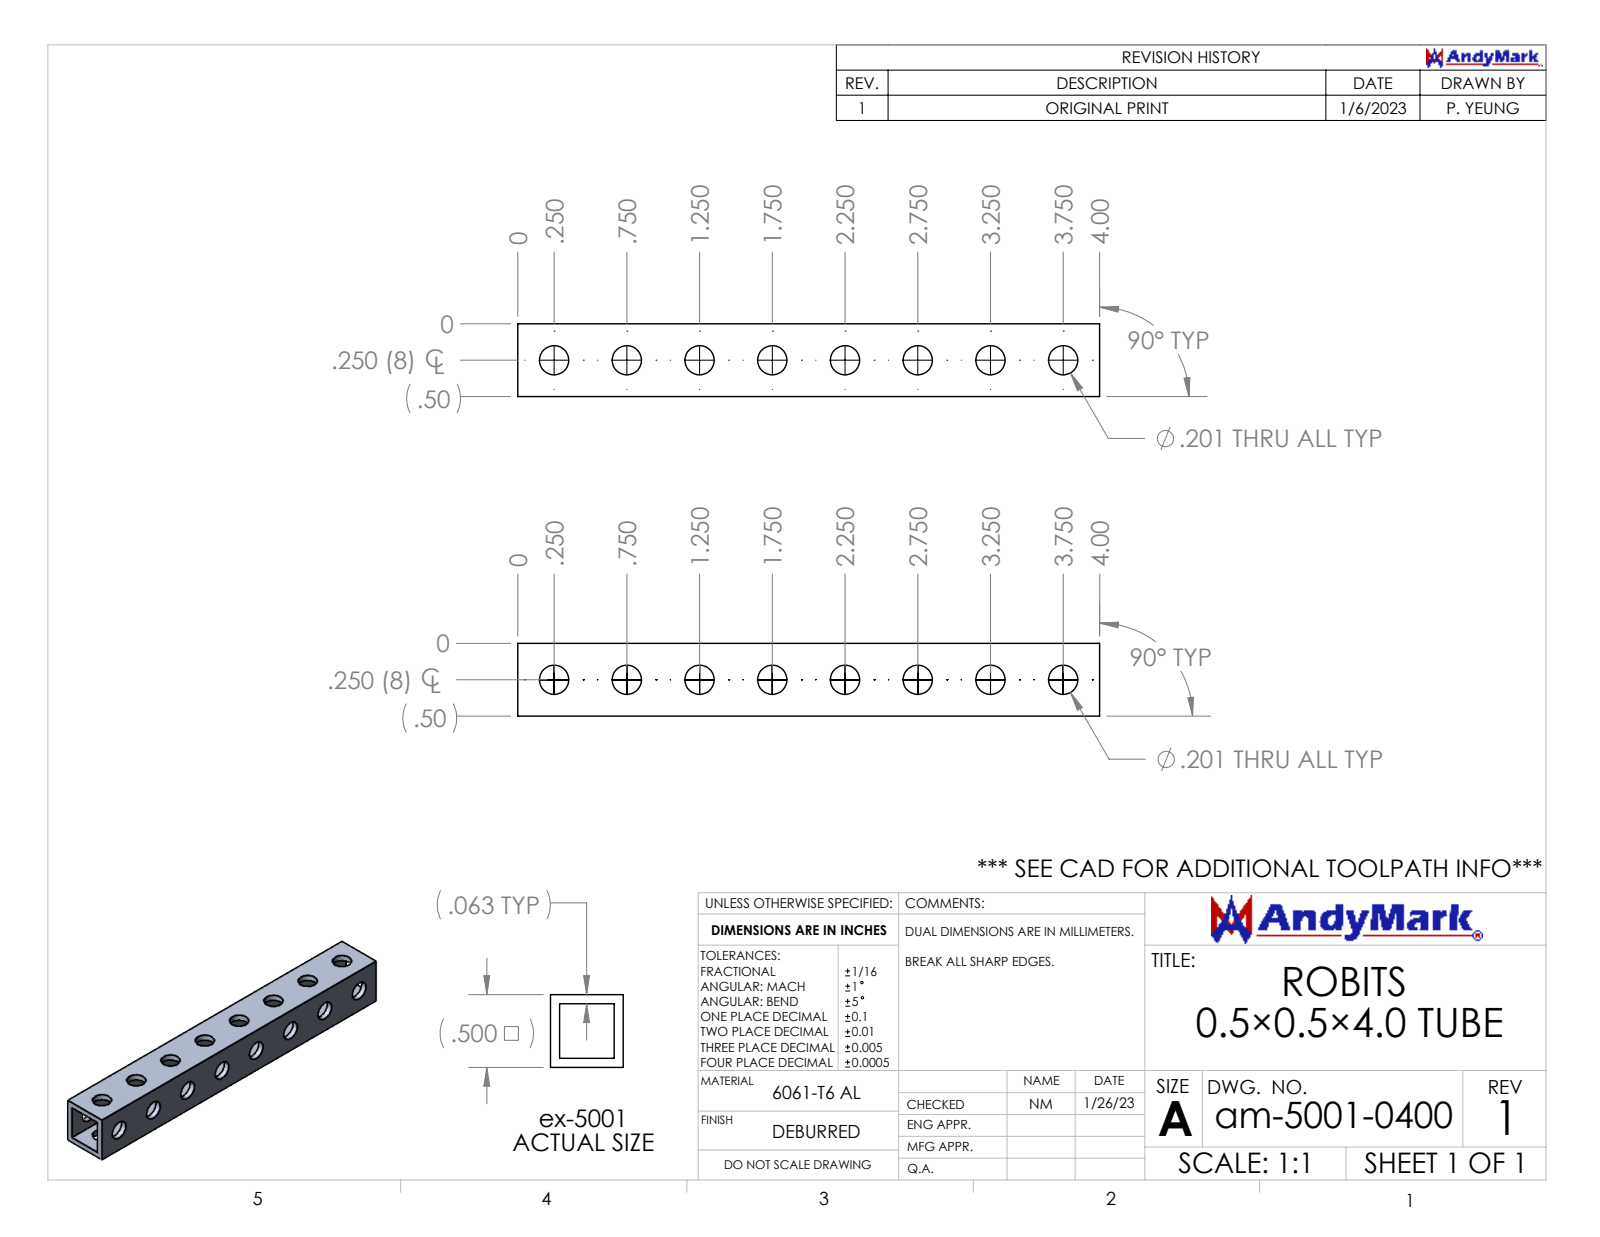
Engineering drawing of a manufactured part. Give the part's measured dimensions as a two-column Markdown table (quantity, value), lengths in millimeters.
| quantity | value |
| --- | --- |
| part name | am-5001-0400 RoBits 0.5×0.5×4.0 Tube |
| STEP written by | SolidWorks 2022 (CONFIG_CONTROL_DESIGN) |
| units | millimeters |
| bodies | 1 solid, 74 faces (10 planar, 64 cylindrical, 0 other) |
| overall size | 101.6 × 12.7 × 12.7 |
| volume | 6 130 mm³ |
| surface area | 8 677 mm² |
| round holes (diameter × count) | 5.1 × 16 |
| main face-to-face distances | 1.6, 11.1, 12.7, 9.5, 101.6 |
| hole center spacings | 12.7, 25.4, 38.1, 50.8, 63.5, 76.2, 88.9 |
